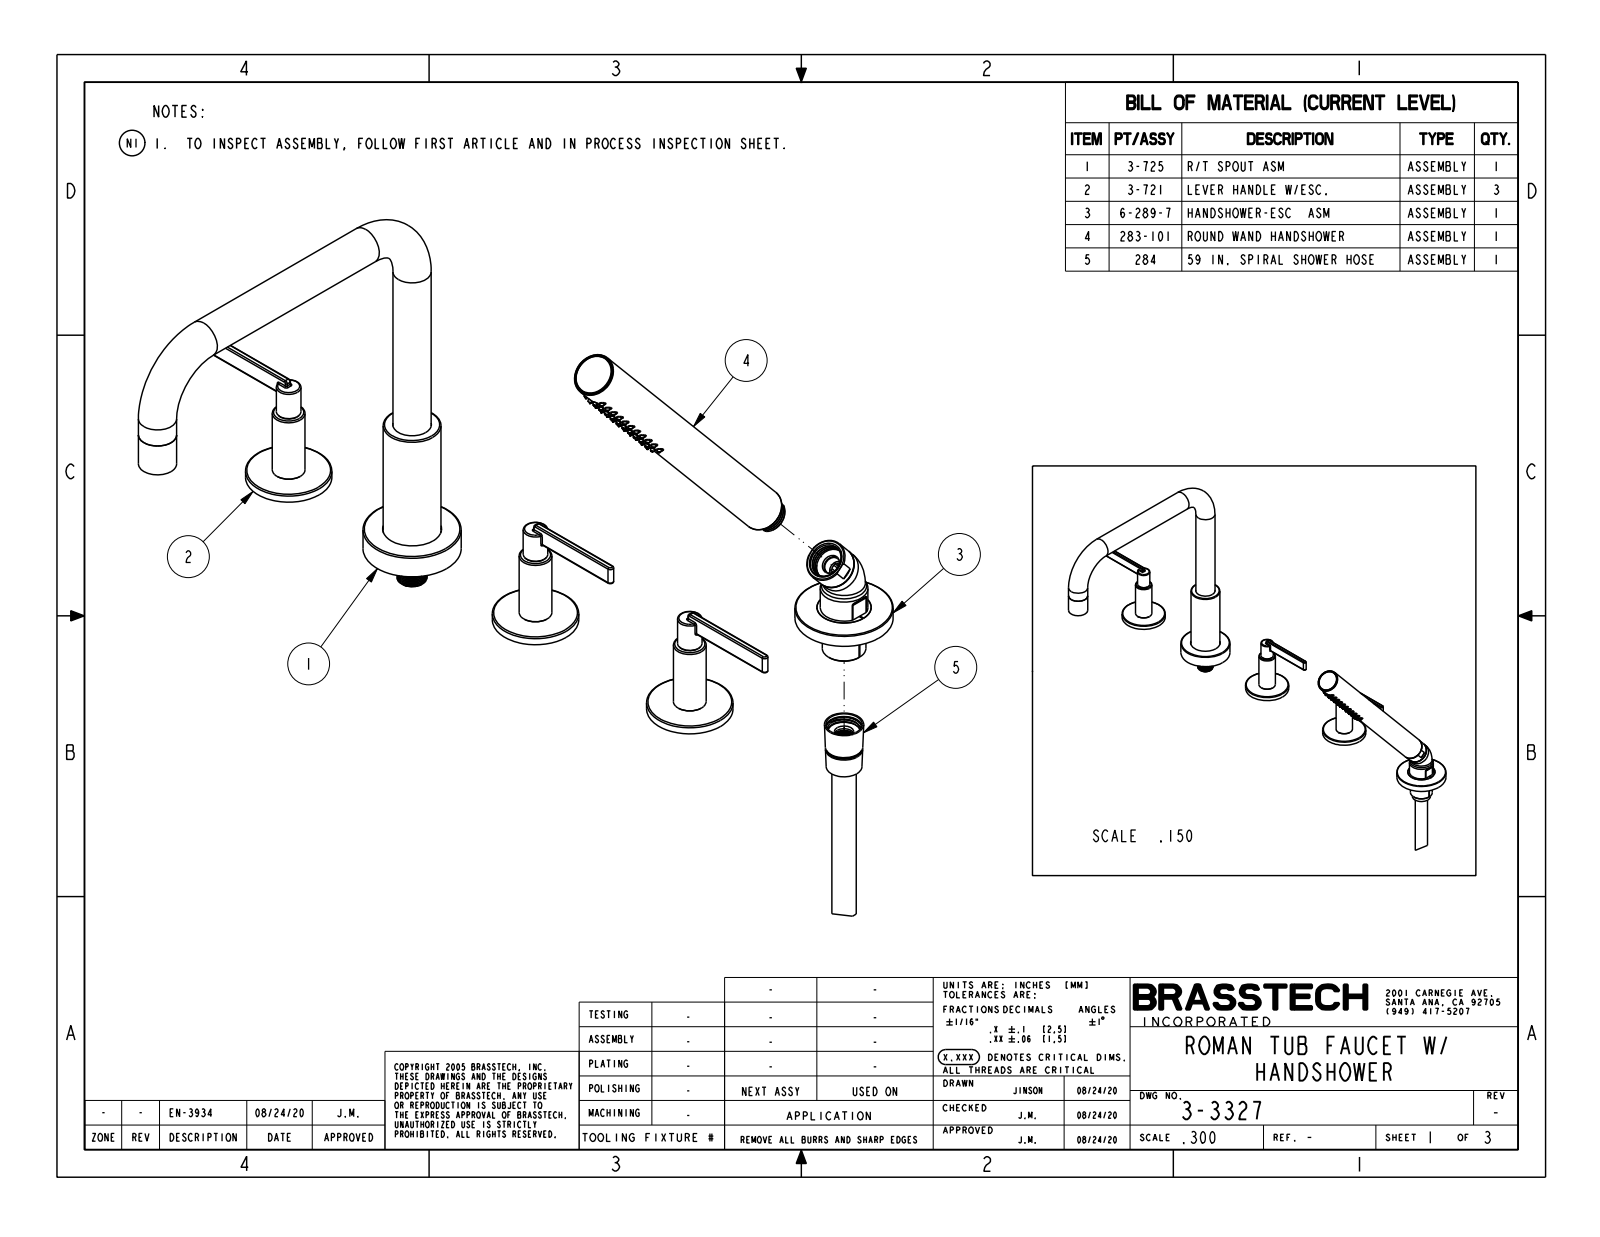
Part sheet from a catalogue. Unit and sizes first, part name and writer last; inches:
Units: inches
Overall size (bounding box): 21.625 × 10.578 × 9.812
Round holes (diameter × count): ⌀0.14 ×44, ⌀0.11 ×3, ⌀0.36 ×3, ⌀0.397 ×3, ⌀0.4 ×3, ⌀0.516 ×3, ⌀0.535 ×3, ⌀0.6 ×3, ⌀0.7 ×3, ⌀0.75 ×3, ⌀0.751 ×3, ⌀1.6 ×3
Round bosses / shafts (diameter × count): ⌀0.73 ×4, ⌀0.68 ×4, ⌀2 ×3, ⌀1.65 ×3, ⌀1 ×3, ⌀0.875 ×3, ⌀0.75 ×3, ⌀0.563 ×3
Partial cylindrical surfaces — rounded edges, fillets, slot ends (radius × count): R0.03 ×21, R0.05 ×6, R0.062 ×4, R0.1 ×4, R0.06 ×3, R0.075 ×3, R0.137 ×3, R0.3 ×1
Main face-to-face distances: 0.15, 0.05, 0.2, 0.3, 0.1, 0.08, 0.07, 0.375, 0.225, 0.15
Hole centre spacings: 0.336, 0.17, 0.447, 0.672, 0.604, 0.29, 0.87, 0.886
Volume: 12.61 in³ · Surface area: 283.8 in²
Bodies: 21 solids, 1790 faces (304 planar, 602 cylindrical, 884 other)
Part name (STEP PRODUCT): 13539; 20-571_ASM; 13540; 13139 (+8 more)
STEP written by: CREO PARAMETRIC BY PTC INC, 2018400 (CONFIG_CONTROL_DESIGN)
